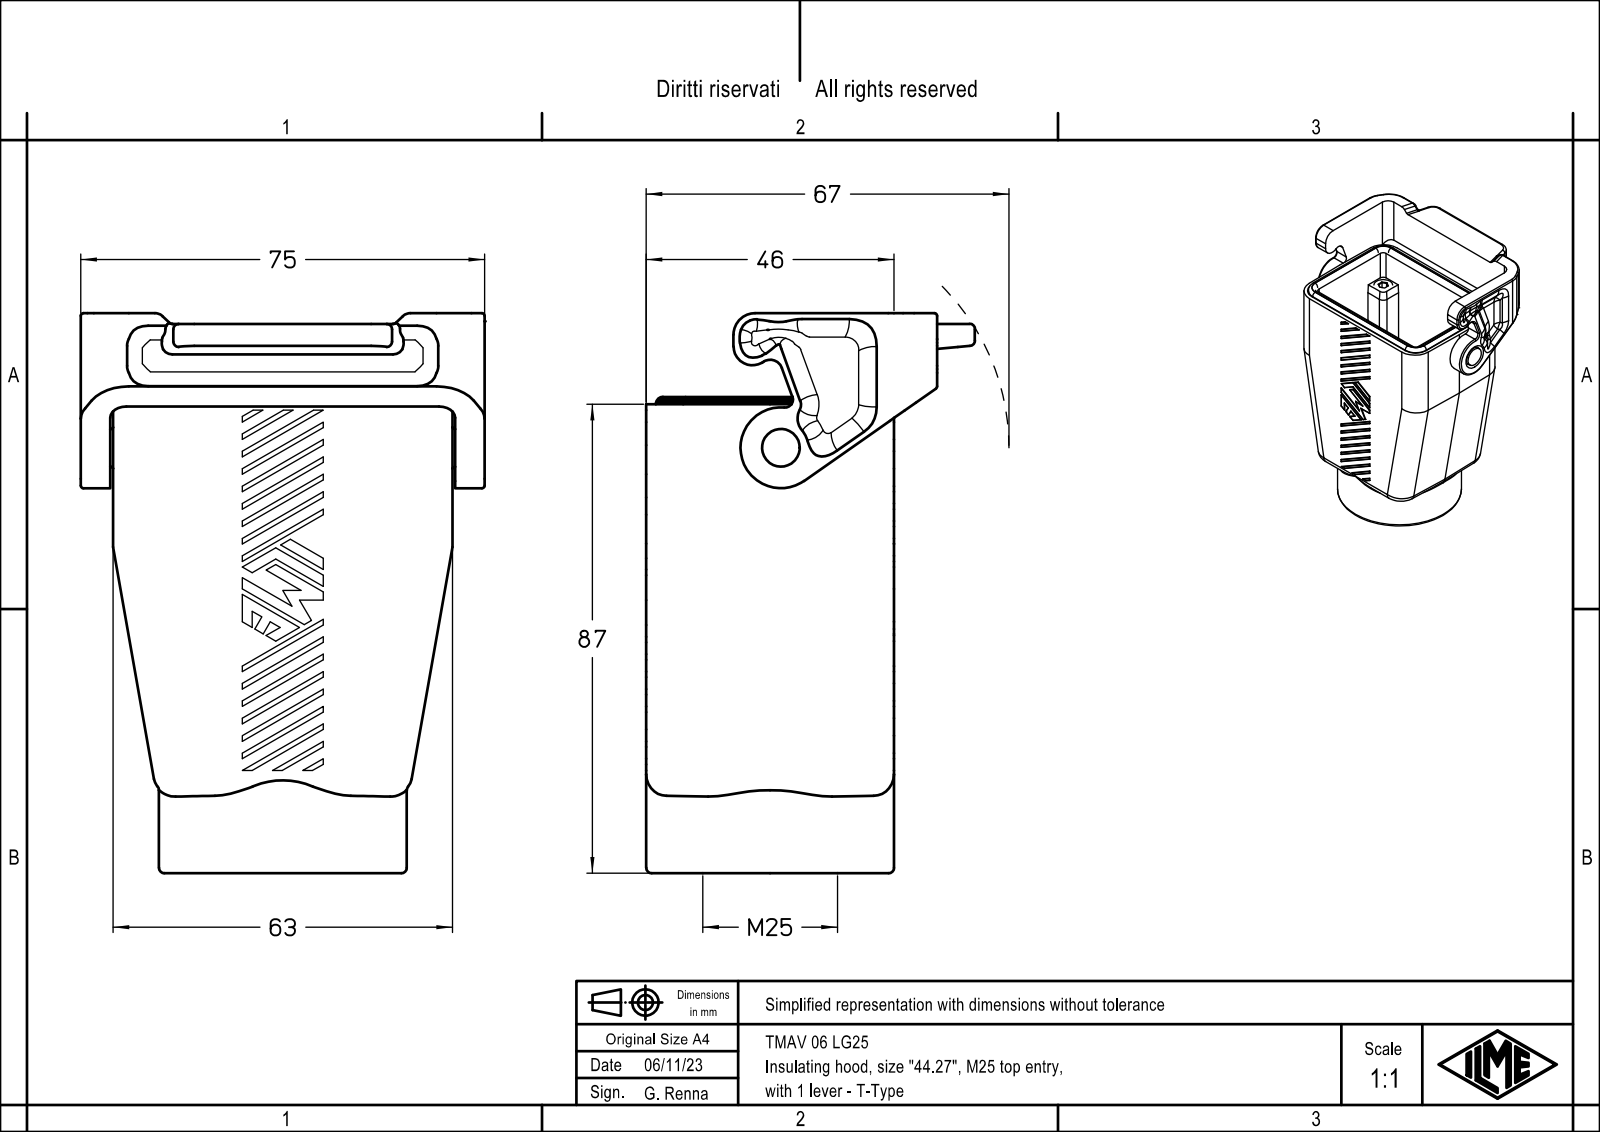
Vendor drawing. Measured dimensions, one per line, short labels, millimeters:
name: TMAV 06 LG25
written by: Creo Elements/Direct Modeling 20.1B 02-Apr-2019 (C) Parametric Technology GmbH (AUTOMOTIVE_DESIGN)
unit: mm
bodies: 1 solid, 546 faces (188 planar, 306 cylindrical, 52 other)
size: 103.9 × 75 × 61.15
volume: 116 497 mm³; area: 40 467 mm²
holes: 1× ⌀21, 1× ⌀23.6
bosses: 1× ⌀46, 1× ⌀7
rounds: 128× R0.15, 13× R3, 10× R2, 8× R1, 8× R1.3, 8× R7, 7× R1.5, 4× R6
face distances: 5.4, 40.6, 46, 35.2, 5.9, 58.1, 3, 20.5, 49, 43.6
